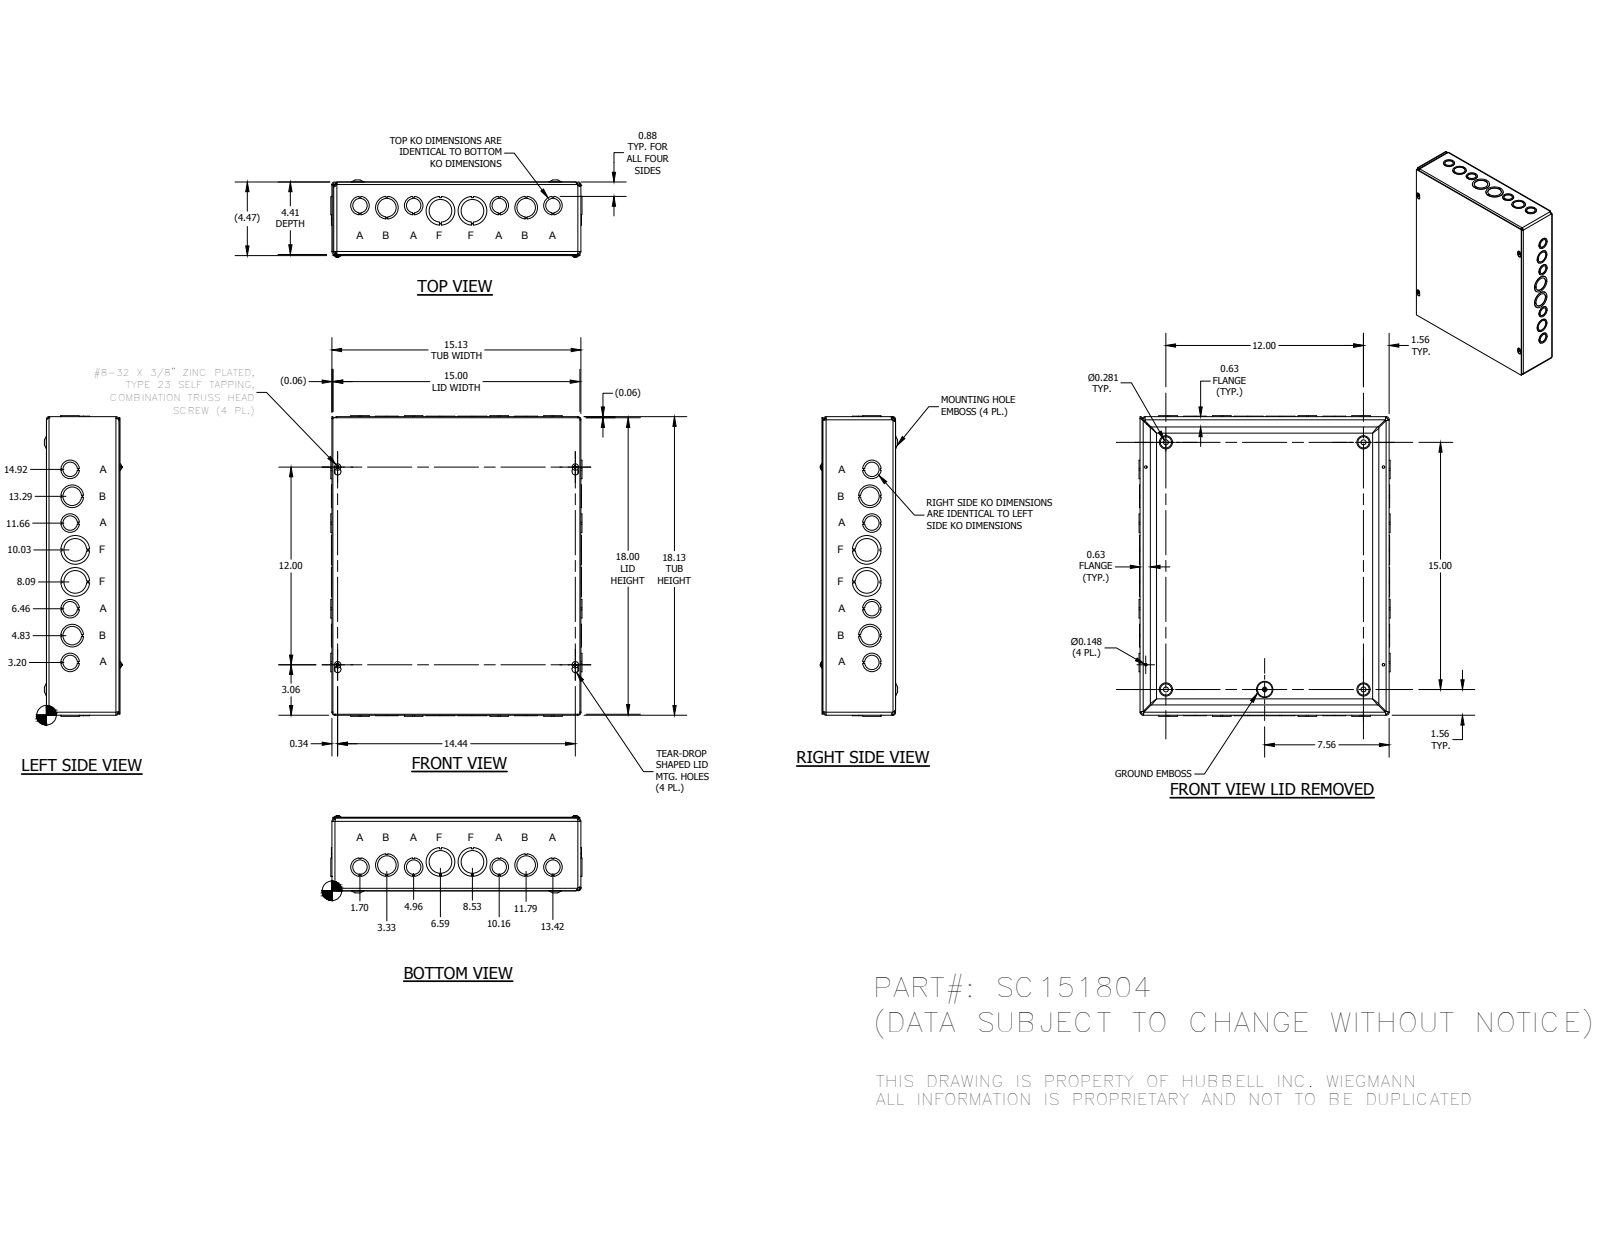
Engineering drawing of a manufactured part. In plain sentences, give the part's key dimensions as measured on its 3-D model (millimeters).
The part is named "SC1518BKP; SC151804WRA; SC1518LID; 34056 (+1 more)". Its 3-D file was written by "Autodesk Inventor 2014 (AUTOMOTIVE_DESIGN)". It is 38 solids with 1254 faces: 837 planar, 259 cylindrical and 158 other. Overall it measures 463.52 by 387.32 by 119.2 millimeters. Round holes: 12 of diameter 28.57, 8 of diameter 22.22, 8 of diameter 34.92, 4 of diameter 3.76, 4 of diameter 7.62, 4 of diameter 44.45, 1 of diameter 4.19. Round bosses or shafts: 4 of diameter 9.75, 4 of diameter 4.17, 1 of diameter 5.8. Partial cylindrical surfaces (rounded edges, fillets, slot ends): 12 of radius 3.17, 8 of radius 4.75, 4 of radius 1.4, 4 of radius 1.57, 4 of radius 2.38, 4 of radius 2.97, 4 of radius 3.15, 4 of radius 3.96. The main face-to-face distances are 1.57, 110.32, 111.89, 1.59, 111.91, 113.48, 382.6, 458.8, 384.17, 381.03. The hole center spacings are 41.52, 42.15, 49.09, 82.94, 91.03, 132.17, 173.51, 214.88.
